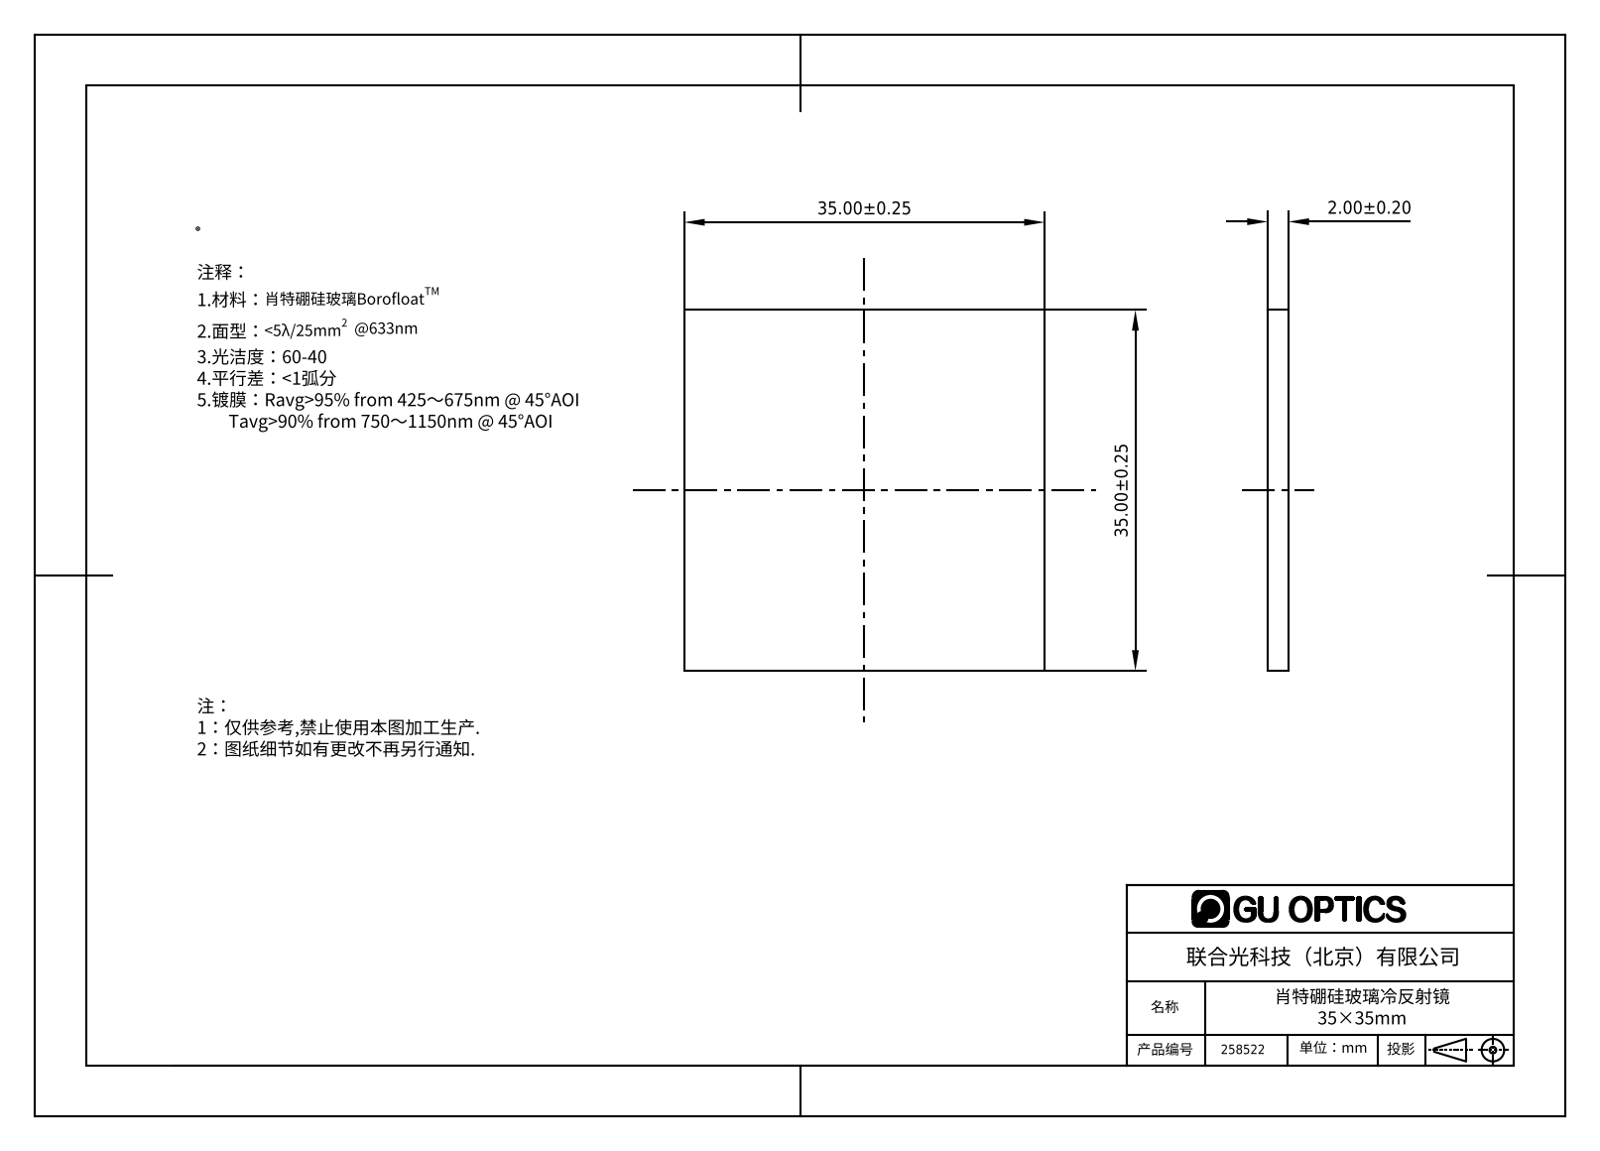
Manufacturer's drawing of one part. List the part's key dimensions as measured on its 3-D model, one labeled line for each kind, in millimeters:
Part name (STEP PRODUCT): 258513
STEP written by: SolidWorks 2016 (AUTOMOTIVE_DESIGN)
Units: millimetres
Bodies: 1 solid, 6 faces (6 planar, 0 cylindrical, 0 other)
Overall size (bounding box): 35 × 35 × 2
Volume: 2 450 mm³ · Surface area: 2 730 mm²
Main face-to-face distances: 2, 35
